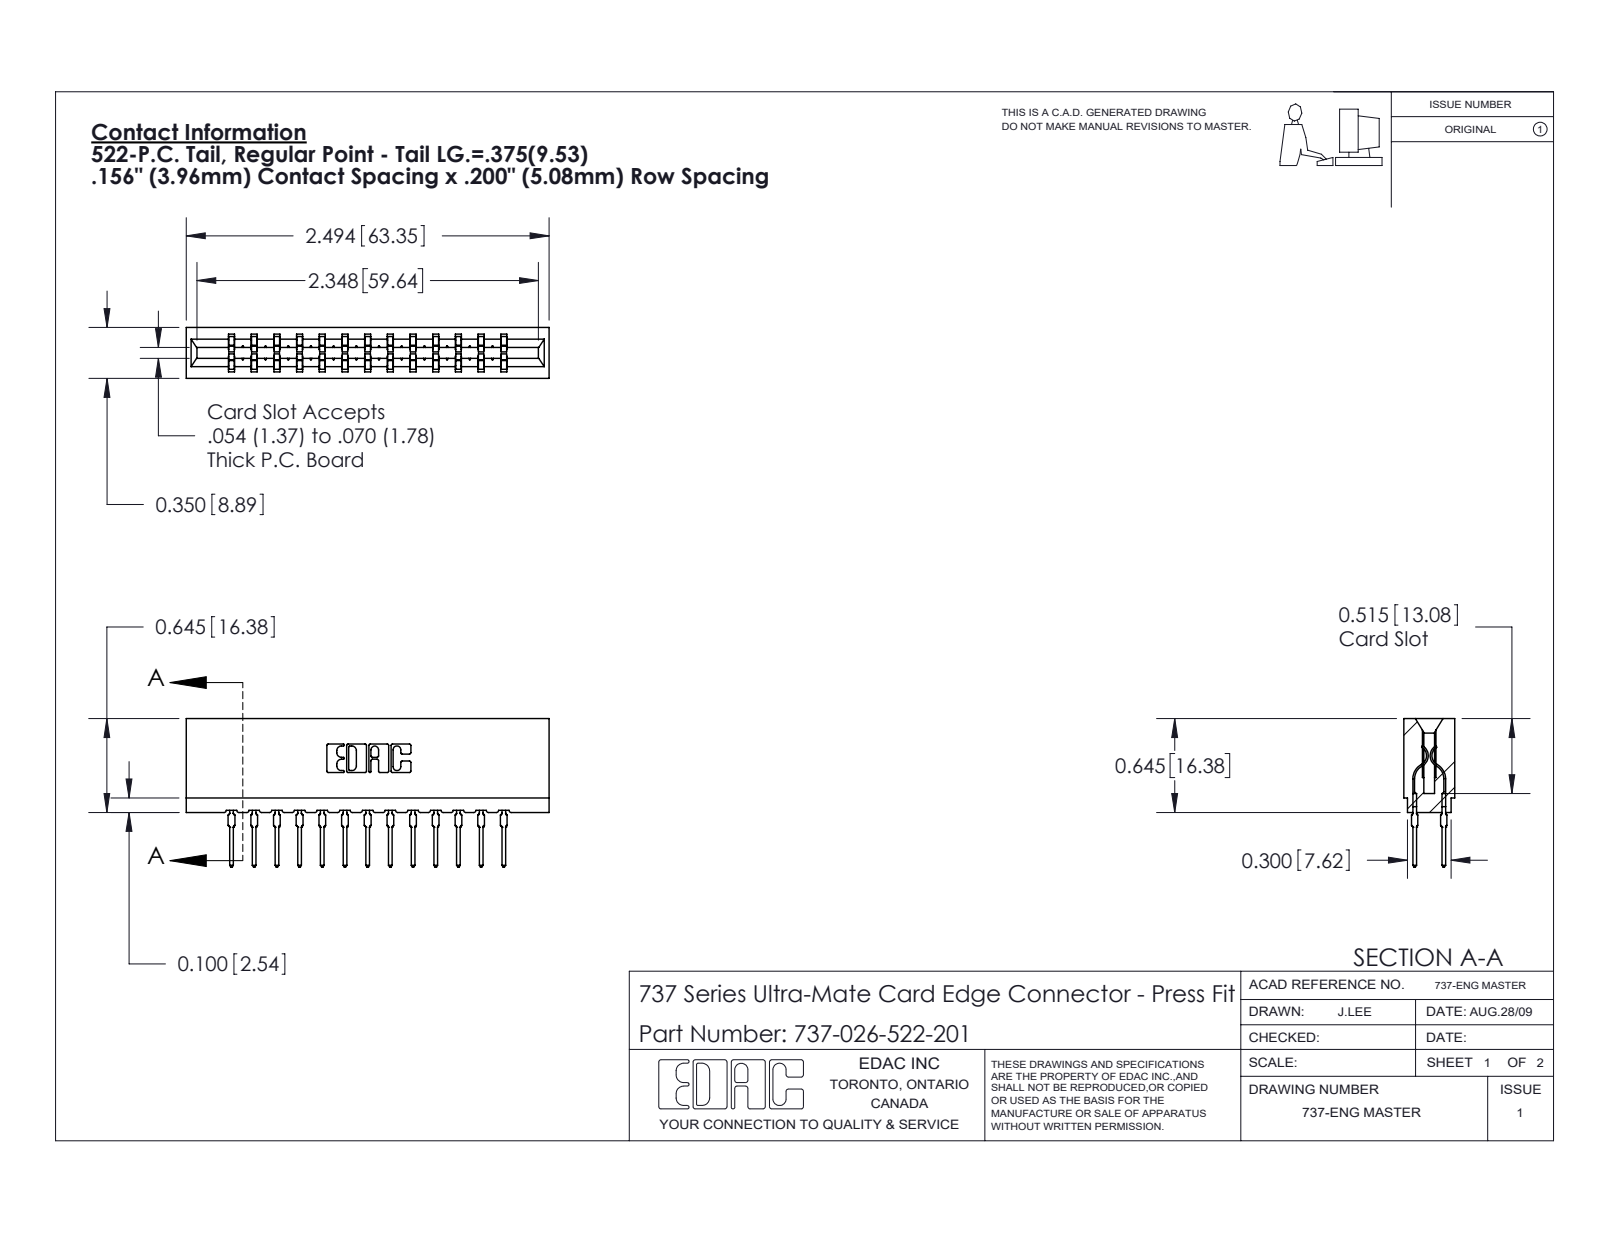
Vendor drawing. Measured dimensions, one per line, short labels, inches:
name: 745-292-001_522; 737-026-522-201; 737 Part_Insulator Option - 01
written by: SolidWorks 2020 (CONFIG_CONTROL_DESIGN)
unit: in
bodies: 27 solids, 2434 faces (1263 planar, 495 cylindrical, 676 other)
size: 2.494 × 1.021 × 0.35
volume: 0.395 in³; area: 13.74 in²
rounds: 52× R0.021, 26× R0.015, 22× R0.01, 8× R0.005, 8× R0.011, 6× R0.007, 6× R0.031, 3× R0.026
face distances: 0.138, 0.212, 0.156, 0.35, 0.312, 0.624, 0.468, 0.78, 0.074, 0.063
